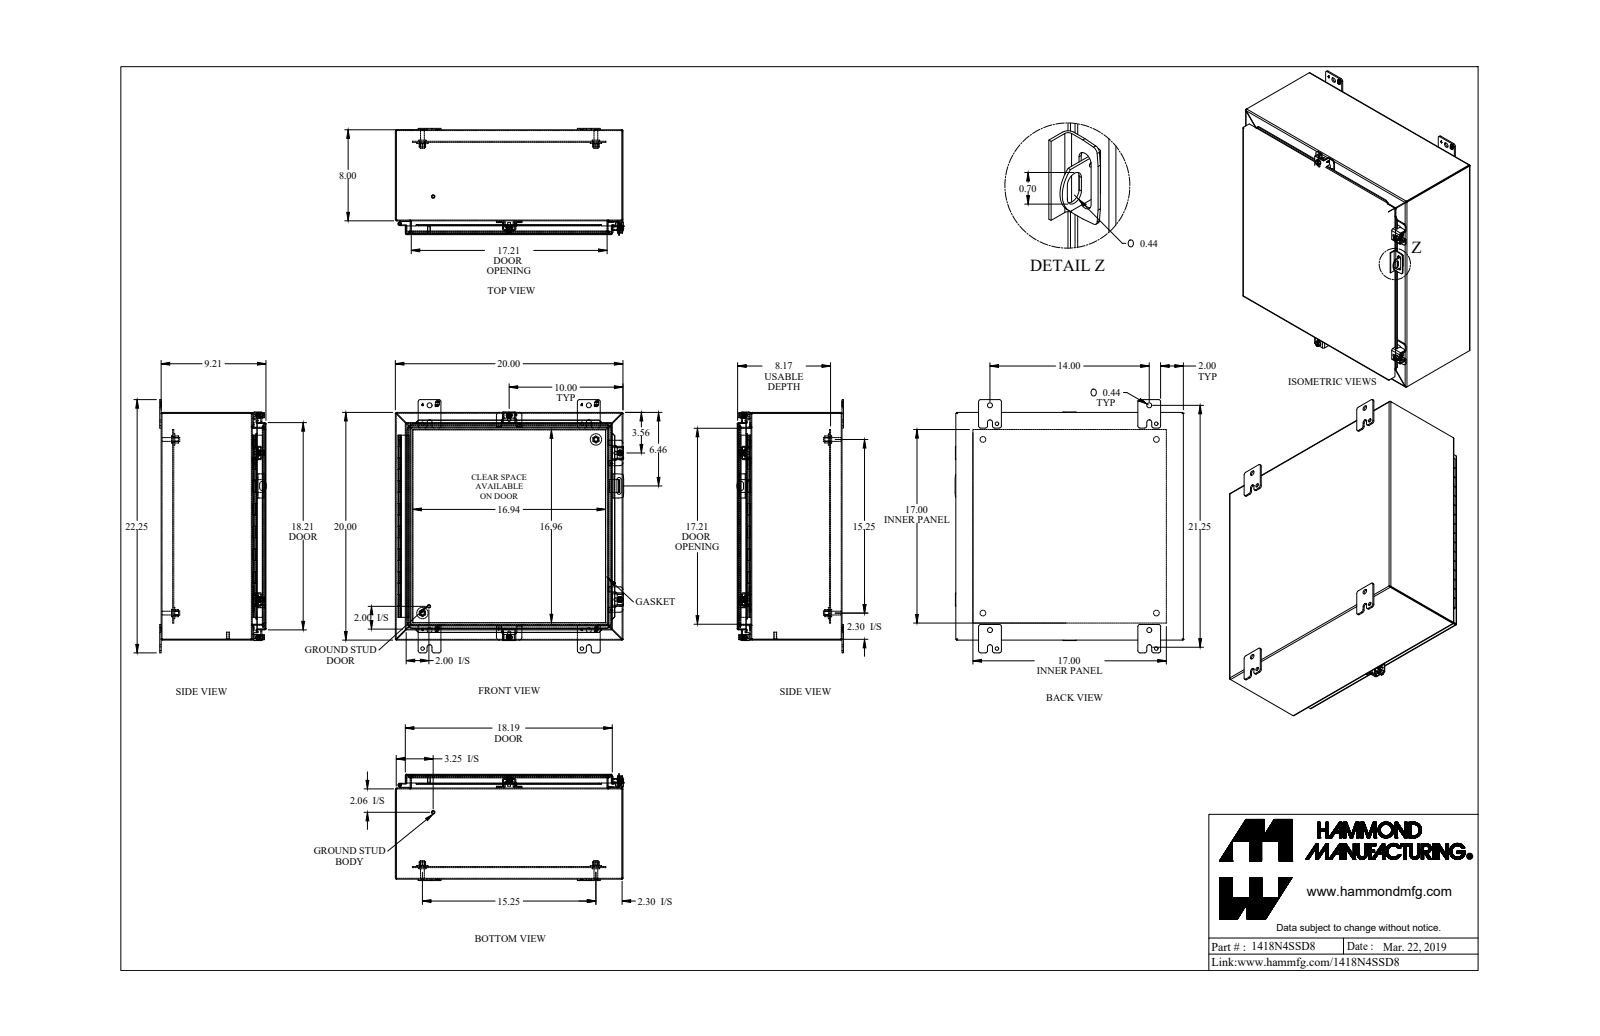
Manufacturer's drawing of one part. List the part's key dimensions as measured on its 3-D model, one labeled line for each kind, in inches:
Part name (STEP PRODUCT): 1418N4SSD8_Default
STEP written by: SolidWorks 2019 (CONFIG_CONTROL_DESIGN)
Units: inches
Bodies: 39 solids, 1454 faces (905 planar, 457 cylindrical, 92 other)
Overall size (bounding box): 22.25 × 20.063 × 9.375
Volume: 156.9 in³ · Surface area: 4 154 in²
Round holes (diameter × count): ⌀0.213 ×4, ⌀0.265 ×4, ⌀0.313 ×4, ⌀0.375 ×4, ⌀0.437 ×4, ⌀0.5 ×4, ⌀0.307 ×2, ⌀0.445 ×2, ⌀0.125 ×1, ⌀0.187 ×1
Round bosses / shafts (diameter × count): ⌀0.65 ×4, ⌀0.5 ×4, ⌀0.39 ×4, ⌀0.375 ×4, ⌀0.332 ×4, ⌀0.244 ×4, ⌀1 ×2, ⌀0.313 ×2
Partial cylindrical surfaces — rounded edges, fillets, slot ends (radius × count): R0.188 ×26, R0.036 ×24, R0.108 ×24, R0.048 ×21, R0.143 ×21, R0.25 ×20, R0.045 ×8, R0.125 ×8
Main face-to-face distances: 0.072, 19.928, 9.066, 9.138, 9.138, 0.072, 9.21, 0.937, 19.856, 20
Hole centre spacings: 15.25, 7.916, 14, 18.975, 22.237, 2.434, 3.065, 16.762
